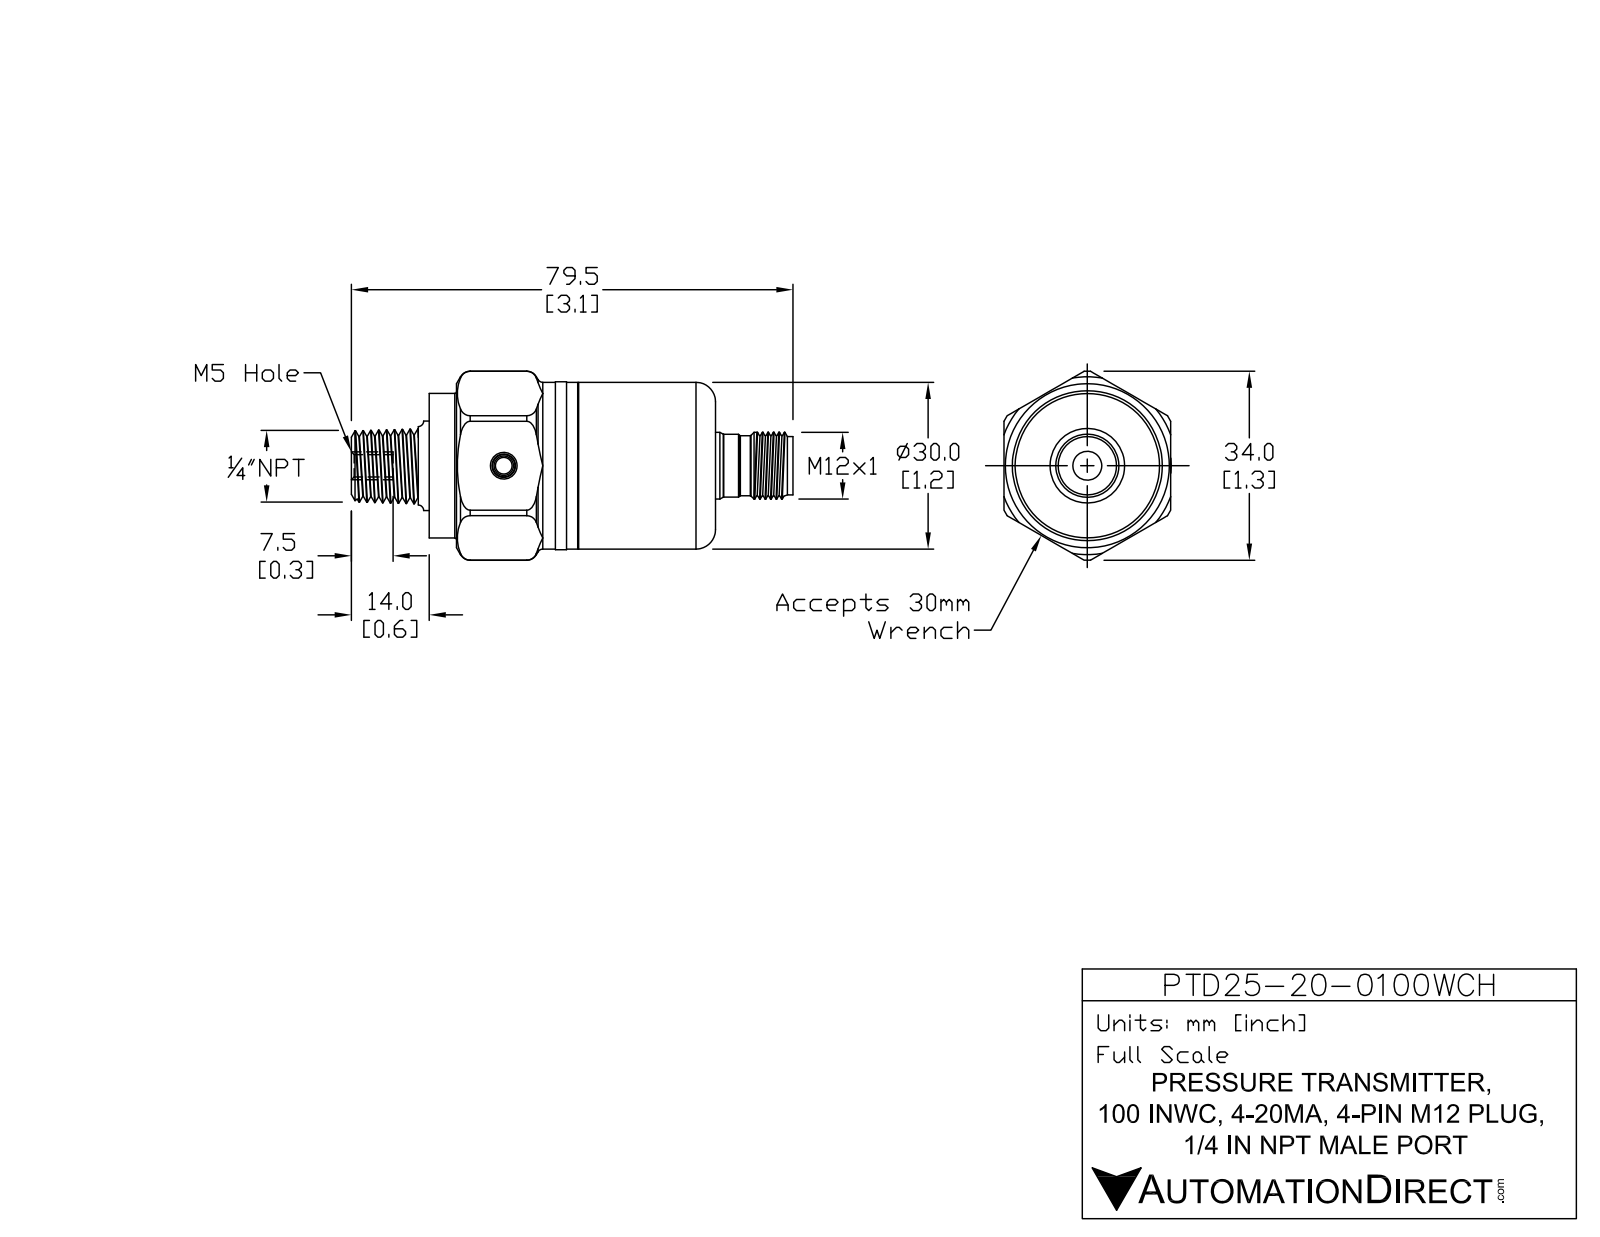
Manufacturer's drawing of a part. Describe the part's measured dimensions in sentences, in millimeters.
The part is named "PTD25-20-0100WCH". Its 3-D file was written by "SolidWorks 2017 (AUTOMOTIVE_DESIGN)". It is 1 solid with 124 faces: 36 planar, 59 cylindrical and 29 other. Overall it measures 79.5 by 33.78 by 31.7 millimeters. Its volume is 39 212 cubic millimeters and its surface area 8 088 square millimeters. Round holes: 1 of diameter 4, 1 of diameter 8.5. Round bosses or shafts: 1 of diameter 30.05, 1 of diameter 30, 1 of diameter 25.96, 1 of diameter 14, 1 of diameter 13.5, 1 of diameter 12. Partial cylindrical surfaces (rounded edges, fillets, slot ends): 1 of radius 3.76, 1 of radius 16.95. The main face-to-face distances are 51, 29.98, 30, 48, 3, 65, 17, 14, 30.01, 5.65.
